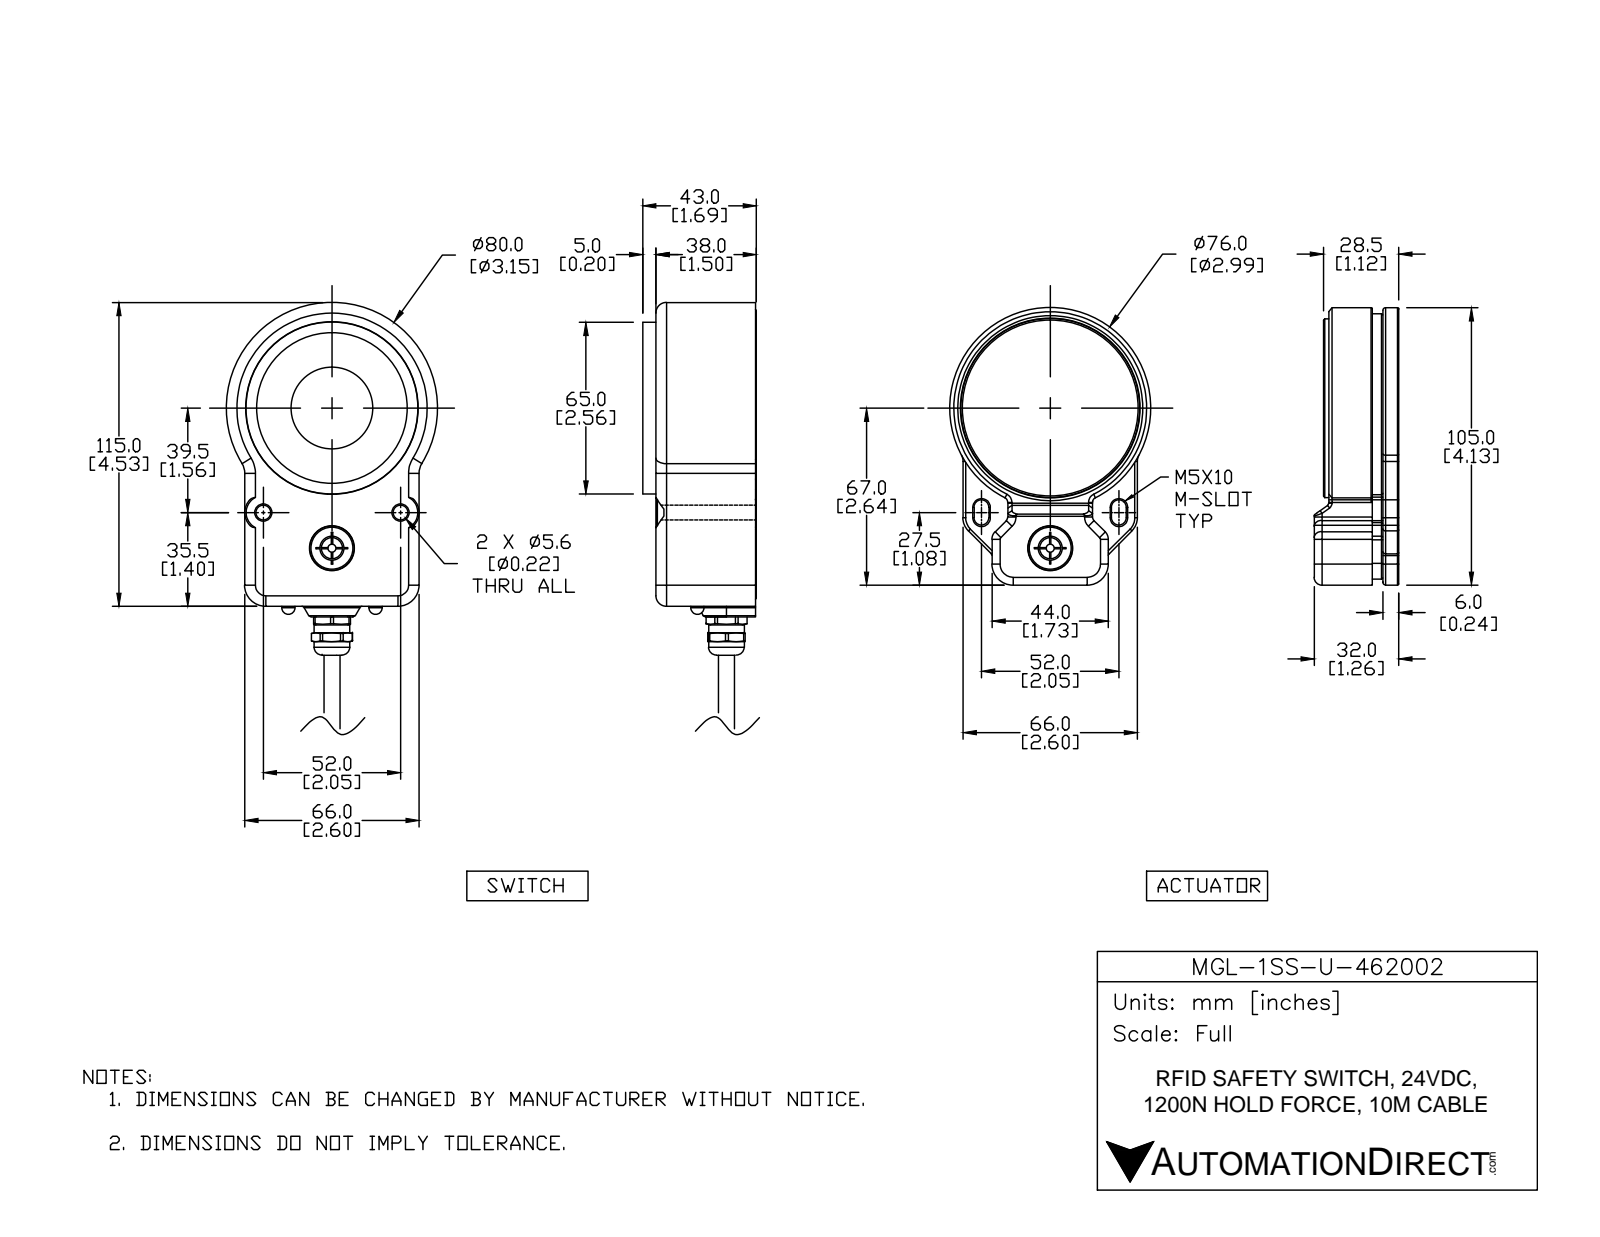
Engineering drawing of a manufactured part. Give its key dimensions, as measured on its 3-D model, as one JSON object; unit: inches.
{"part_name": "MGL-1SS-U-462002_2; MGL-1SS-U-462002_1; MGL-1SS-U-462002", "step_written_by": "SolidWorks 2017 (AUTOMOTIVE_DESIGN)", "units": "inches", "bodies": {"solids": 19, "faces": 1647, "planar": 423, "cylindrical": 679, "other": 545}, "overall_size": [8.465, 3.15, 2.854], "volume_in3": 19.52, "surface_area_in2": 219.9, "round_holes": [[0.098, 8], [0.13, 6], [0.197, 6], [0.453, 5], [0.157, 3], [0.315, 3], [0.354, 3], [0.22, 2], [0.276, 2], [0.252, 1], [0.266, 1], [0.268, 1]], "round_bosses_or_shafts": [[0.02, 4], [0.472, 2], [0.228, 2], [0.22, 2], [0.118, 2], [0.047, 2], [2.992, 1], [2.811, 1]], "partial_cylinders_radius": [[0.02, 188], [0.039, 64], [0.079, 26], [0.012, 17], [0.118, 13], [0.157, 12], [0.217, 10], [0.024, 7]], "face_to_face_distances": [0.236, 0.315, 0.098, 0.413, 1.378, 2.303, 1.122, 0.118, 0.354, 2.205], "hole_center_spacings": [1.392, 1.969, 0.984, 1.28, 1.537, 0.787, 1.364, 0.349]}
